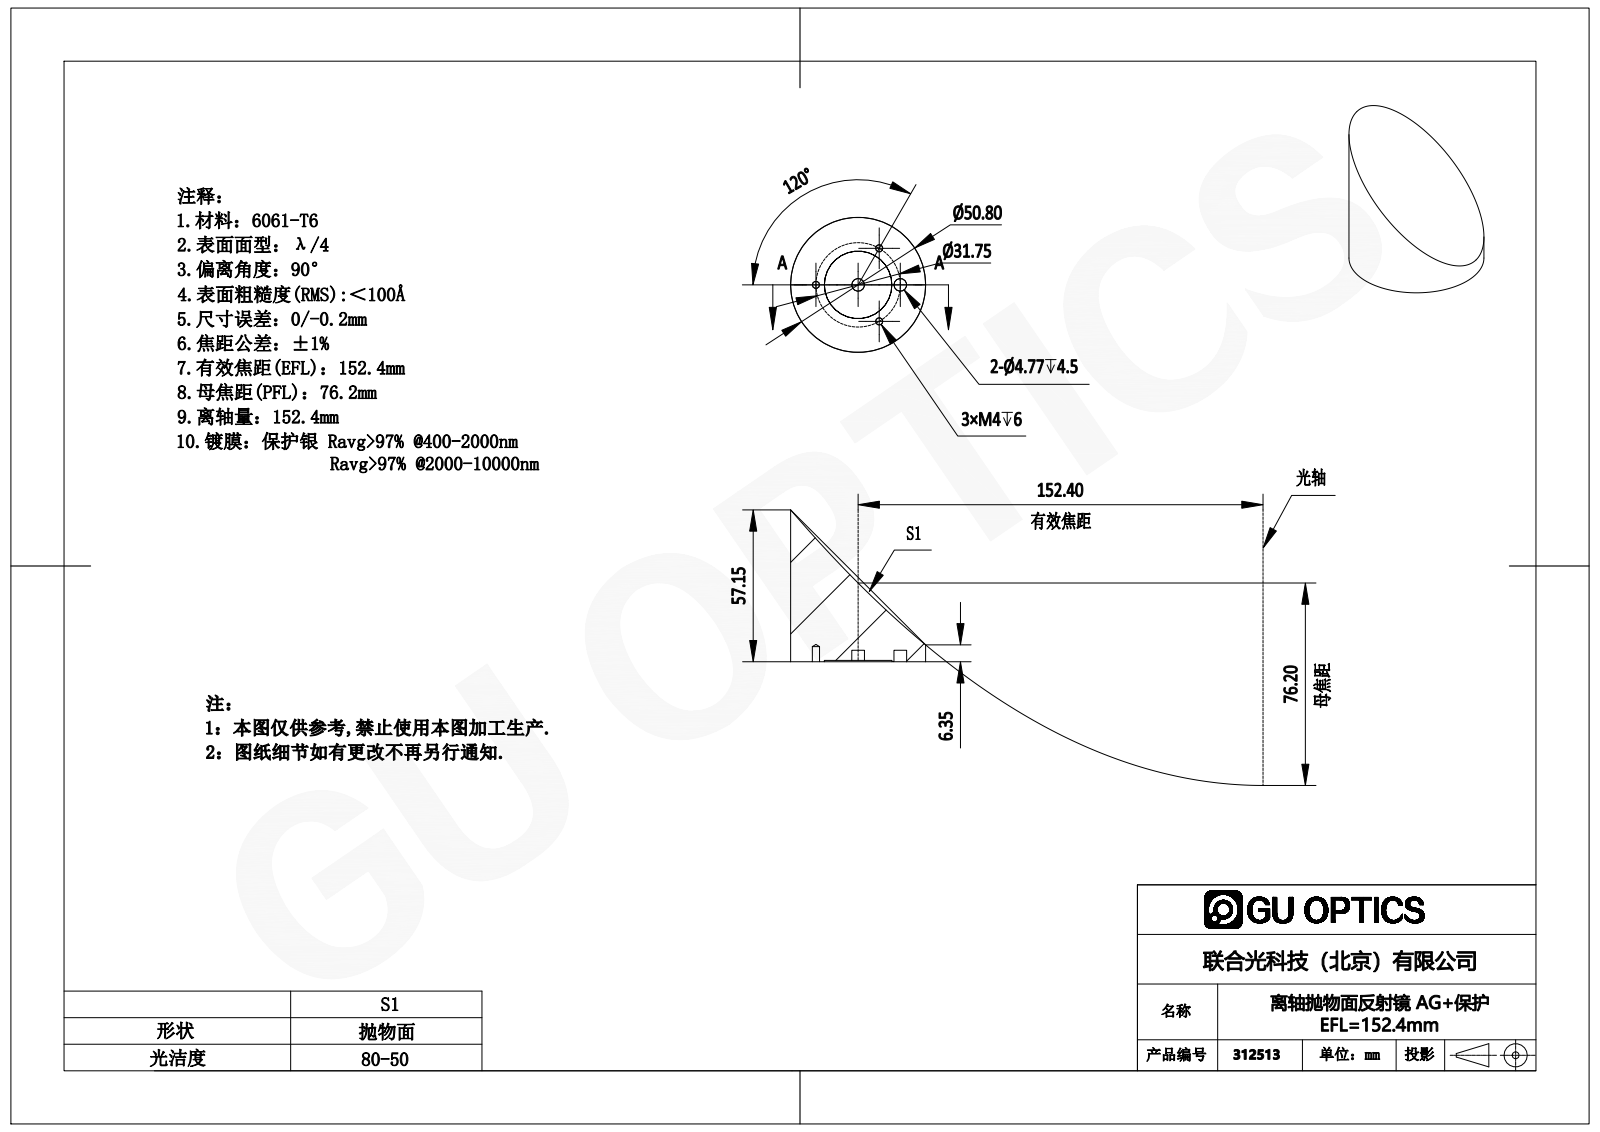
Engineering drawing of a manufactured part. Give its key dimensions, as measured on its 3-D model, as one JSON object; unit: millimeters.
{"part_name": "Ø50_36597", "step_written_by": "SolidWorks 2018 (CONFIG_CONTROL_DESIGN)", "units": "millimeters", "bodies": {"solids": 1, "faces": 26, "planar": 4, "cylindrical": 14, "other": 8}, "overall_size": [57.15, 50.8, 50.8], "volume_mm3": 61701, "surface_area_mm2": 10278, "round_holes": [[2.71, 3], [4.77, 1], [4.78, 1], [25.4, 1]], "round_bosses_or_shafts": [[50.8, 1]], "face_to_face_distances": [0.51, 4.32, 3.81], "hole_center_spacings": [15.88, 27.5, 31.76]}
